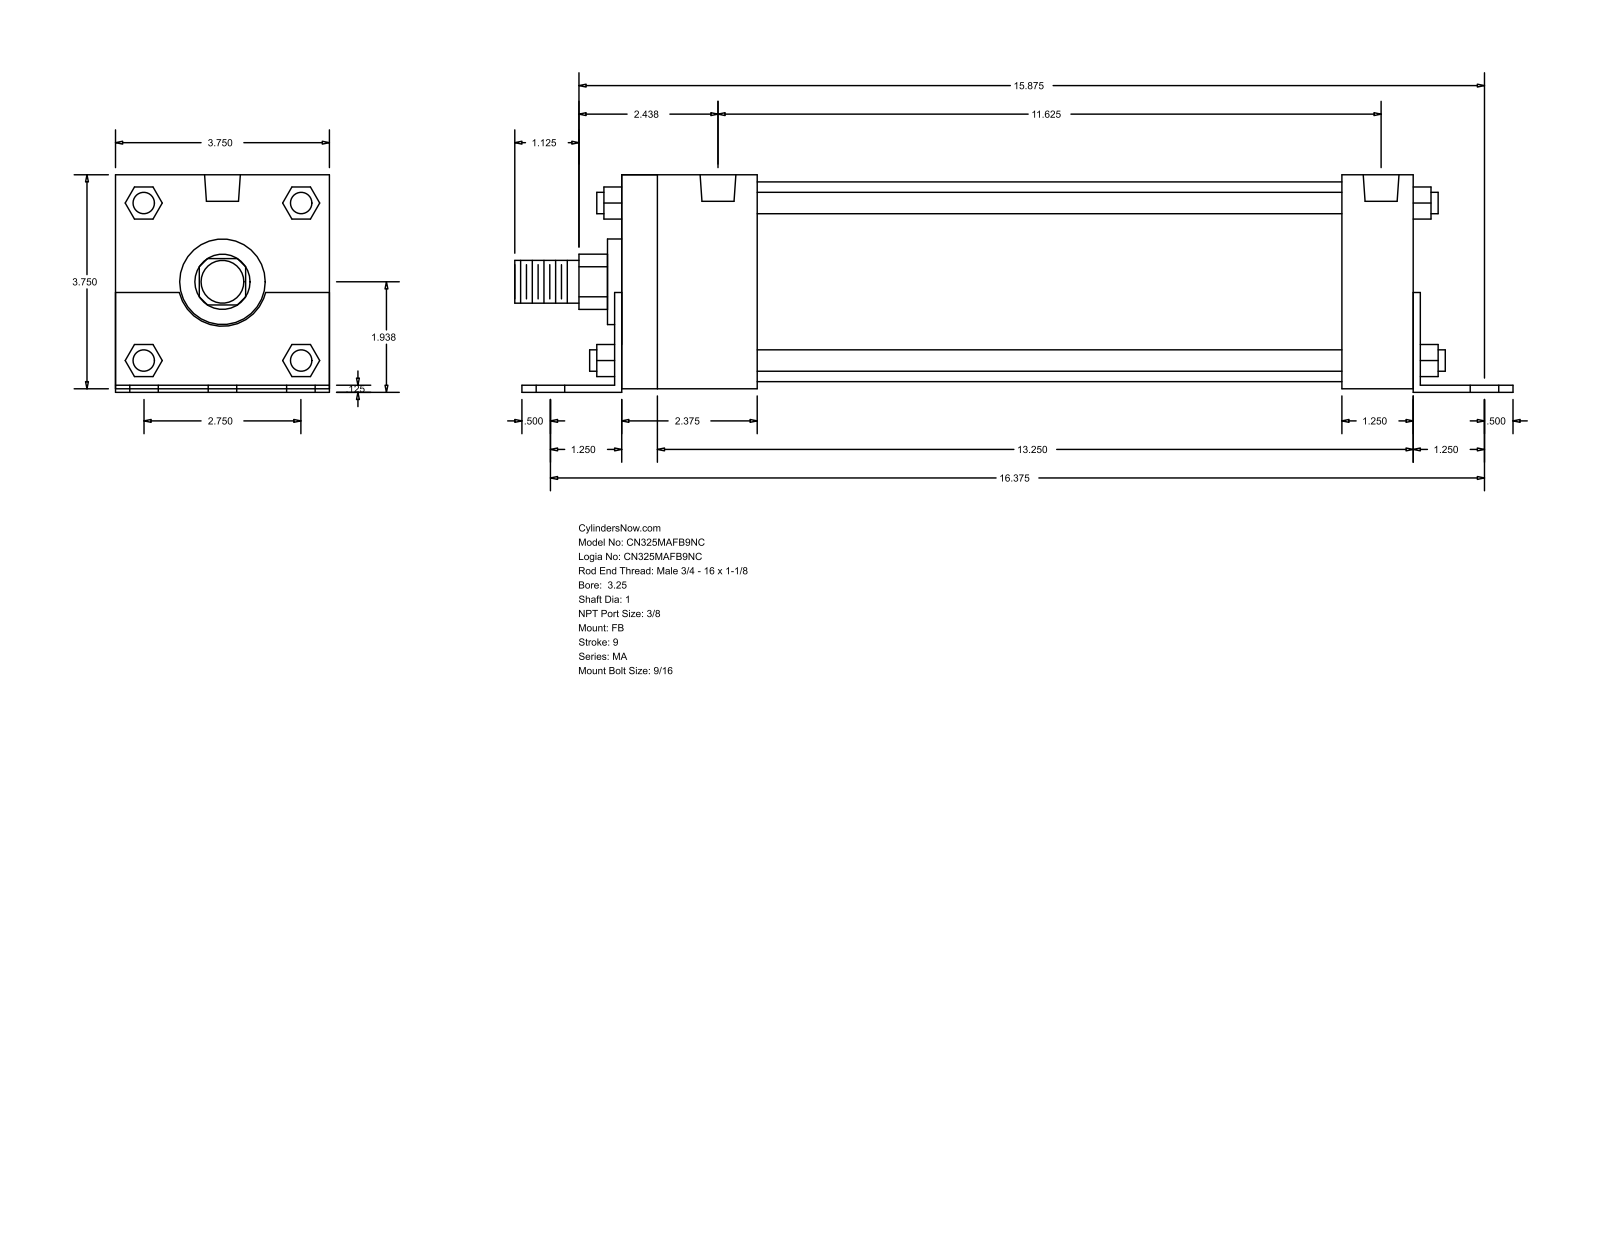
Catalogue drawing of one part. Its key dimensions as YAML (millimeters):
part_name: "MA_FB__0325_1"
step_written_by: "GSSL Pune (CONFIG_CONTROL_DESIGN)"
units: millimeters
bodies: {solids: 0, faces: 140, planar: 105, cylindrical: 35, other: 0}
overall_size: [444.5, 96.84, 95.25]
round_holes:
  - {diameter: 14.29, count: 6}
  - {diameter: 11.11, count: 4}
  - {diameter: 15.93, count: 2}
round_bosses_or_shafts:
  - {diameter: 9.53, count: 4}
  - {diameter: 88.9, count: 1}
  - {diameter: 38.1, count: 1}
  - {diameter: 25.4, count: 1}
  - {diameter: 19.05, count: 1}
partial_cylinders:
  - {radius: 12.29, count: 1}
  - {radius: 19.81, count: 1}
face_to_face_distances: [95.24, 3.17, 1.59, 96.83, 1.58, 93.66, 355.6, 352.43, 358.77, 323.85]
hole_center_spacings: [34.92, 417.39, 415.93, 4.76, 57.78, 61.64, 69.84, 82.38]
